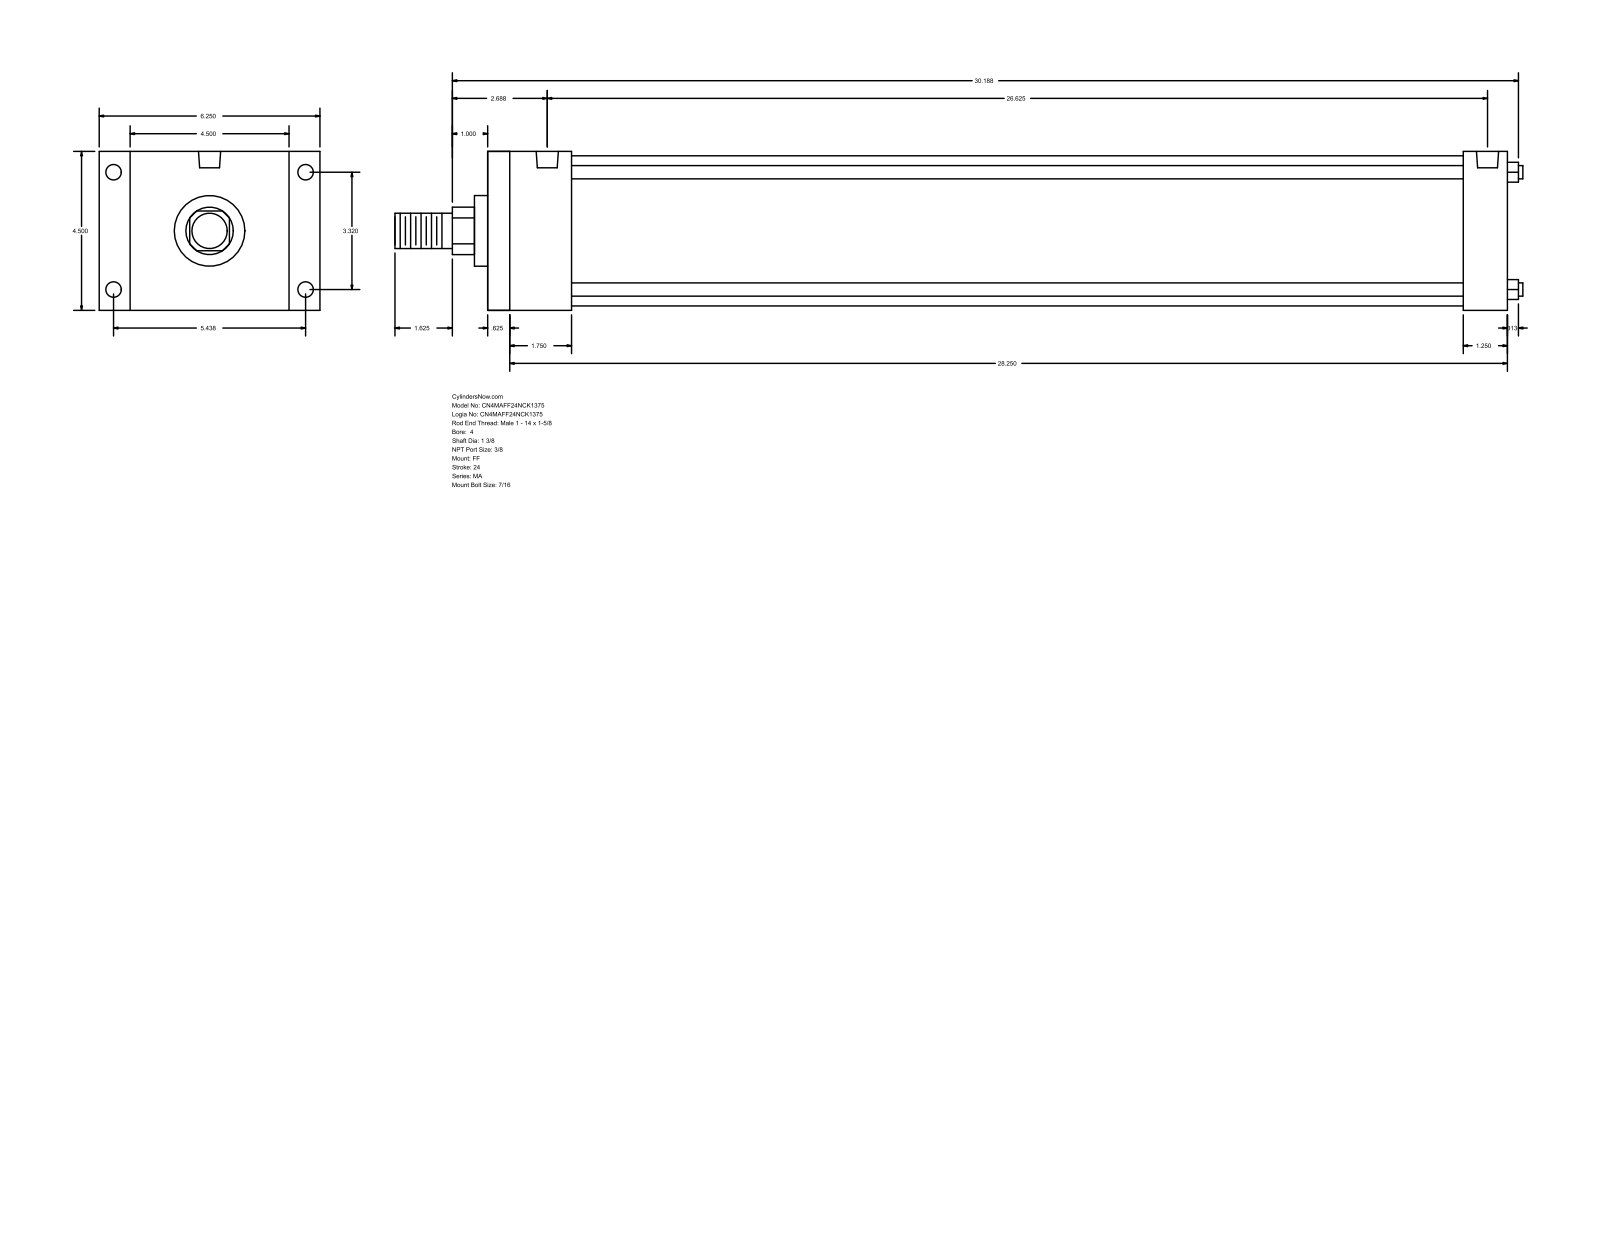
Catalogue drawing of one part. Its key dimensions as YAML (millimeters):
part_name: "MA_FF__0400_1.375"
step_written_by: "GSSL Pune (CONFIG_CONTROL_DESIGN)"
units: millimeters
bodies: {solids: 0, faces: 92, planar: 64, cylindrical: 28, other: 0}
overall_size: [811.21, 158.75, 114.3]
round_holes:
  - {diameter: 11.11, count: 8}
  - {diameter: 15.93, count: 2}
round_bosses_or_shafts:
  - {diameter: 9.53, count: 4}
  - {diameter: 107.95, count: 1}
  - {diameter: 50.8, count: 1}
  - {diameter: 34.92, count: 1}
  - {diameter: 25.4, count: 1}
partial_cylinders:
  - {radius: 17.06, count: 1}
face_to_face_distances: [114.3, 733.43, 15.87, 717.56, 22.23, 136.53, 701.68, 685.81, 31.75, 60.32]
hole_center_spacings: [4.77, 84.32, 138.12, 161.82, 666.74, 671.51, 676.28]
